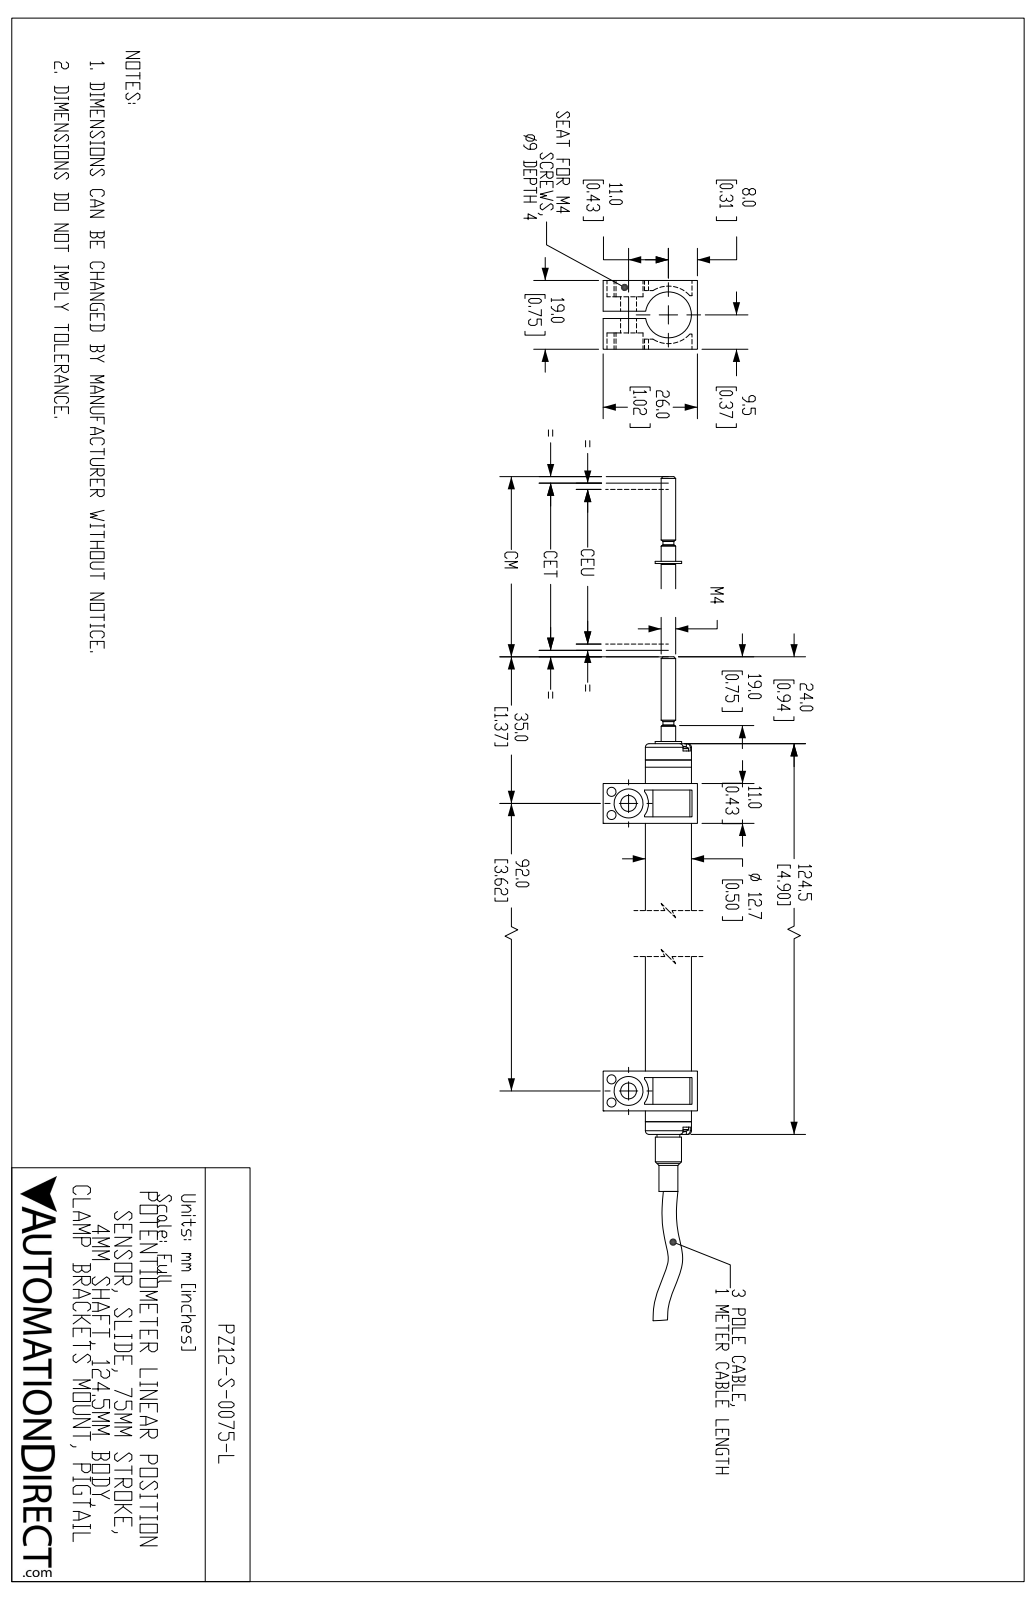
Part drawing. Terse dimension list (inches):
name: PZ12-S-0075-L
written by: SolidWorks 2019 (AUTOMOTIVE_DESIGN)
unit: in
bodies: 14 solids, 594 faces (198 planar, 164 cylindrical, 232 other)
size: 7.872 × 1.024 × 0.748
volume: 1.406 in³; area: 25.28 in²
holes: 4× ⌀0.098, 2× ⌀0.055, 2× ⌀0.059, 2× ⌀0.079, 2× ⌀0.173, 2× ⌀0.315, 1× ⌀0.039, 1× ⌀0.126, 1× ⌀0.138, 1× ⌀0.201, 1× ⌀0.219, 1× ⌀0.236
bosses: 2× ⌀0.126, 2× ⌀0.063, 2× ⌀0.02, 1× ⌀0.5, 1× ⌀0.283, 1× ⌀0.248, 1× ⌀0.205, 1× ⌀0.157
rounds: 4× R0.01, 2× R0.02, 2× R0.026, 2× R0.069, 2× R0.217, 1× R0.017, 1× R0.103, 1× R0.144
face distances: 3.78, 0.433, 0.177, 0.079, 0.335, 0.413, 4.213, 1.024, 3.346, 0.256
hole spacings: 0.224, 3.78, 0.189, 0.197, 0.213, 0.252, 0.322, 3.658
